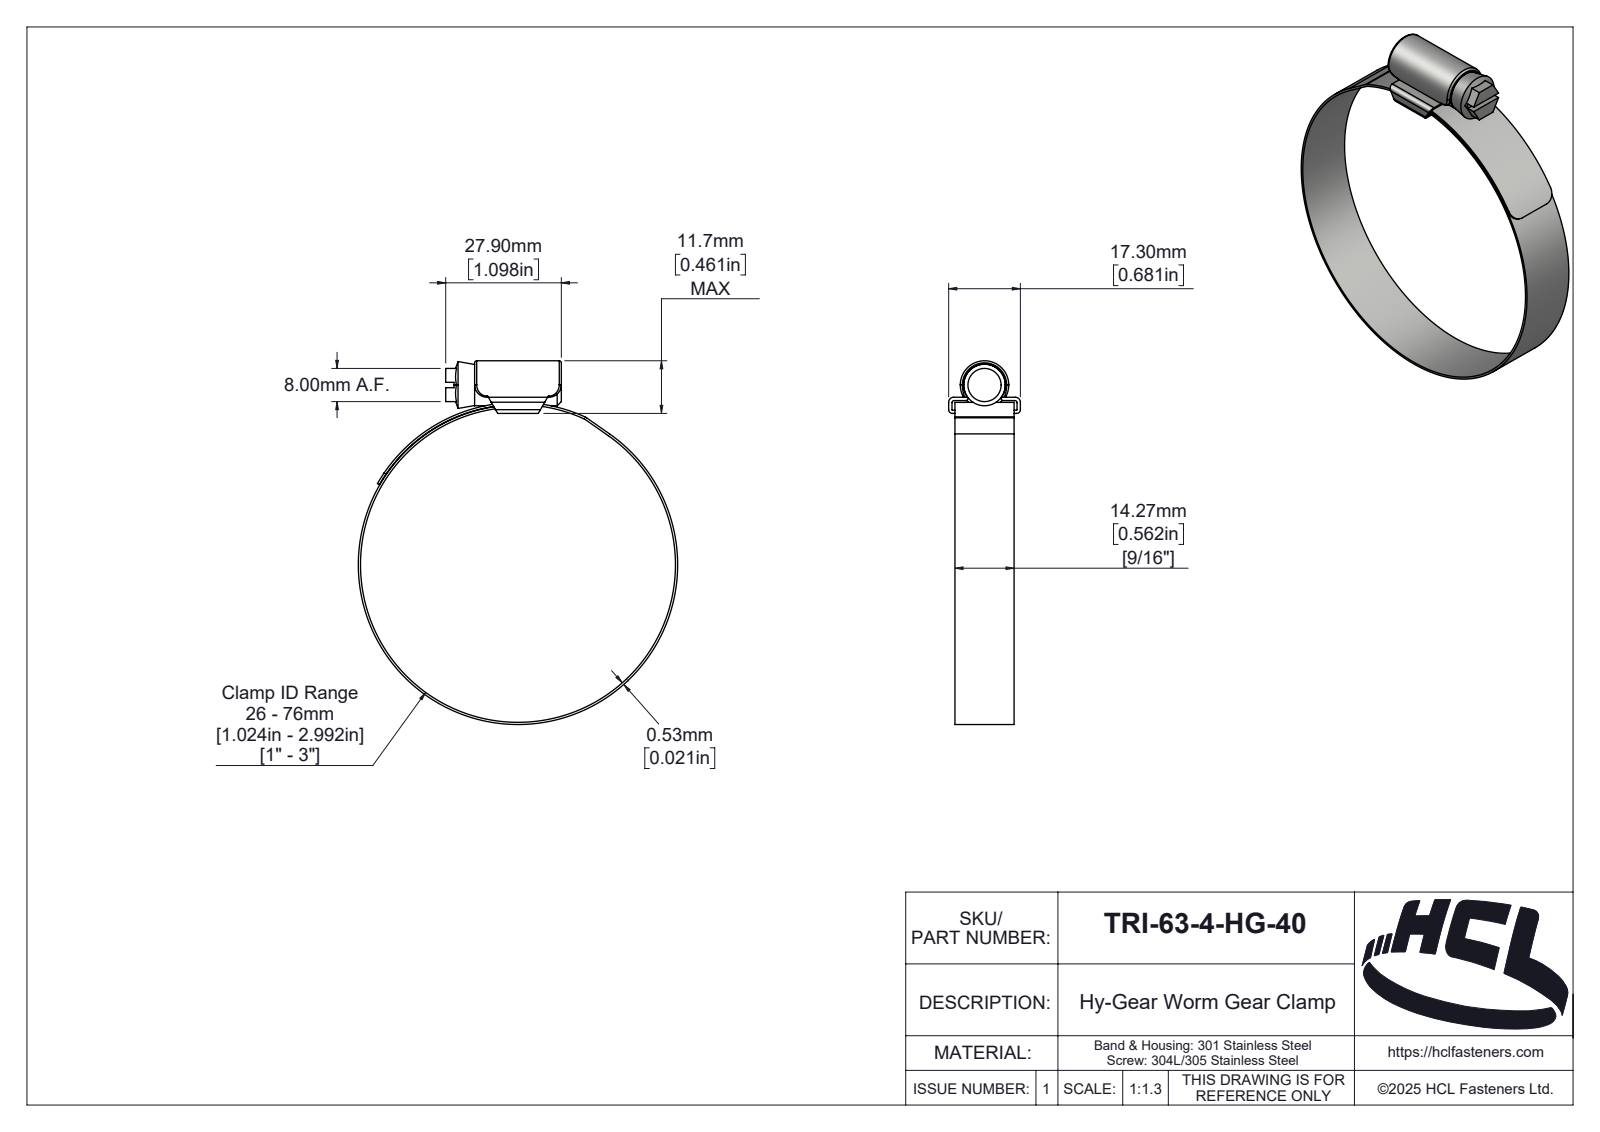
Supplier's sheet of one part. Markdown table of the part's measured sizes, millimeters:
| quantity | value |
| --- | --- |
| part name | TRI-50-0-HG-40 |
| STEP written by | SolidWorks 2025 (AUTOMOTIVE_DESIGN) |
| units | millimeters |
| bodies | 3 solids, 189 faces (39 planar, 89 cylindrical, 61 other) |
| overall size | 87.73 × 77.06 × 17.3 |
| volume | 4 919 mm³ |
| surface area | 11 131 mm² |
| round holes (diameter × count) | 76 × 1 |
| round bosses / shafts (diameter × count) | 77.06 × 1, 10 × 1 |
| partial cylindrical surfaces (radius × count) | 0.5 × 6, 3 × 4, 0.1 × 2, 0.9 × 2, 1.2 × 2, 0.46 × 1, 1.89 × 1, 2 × 1 |
| main face-to-face distances | 0.8, 3.1, 14.26, 0.53, 2.3, 3.9, 27.9, 1.52, 15.78, 16.5 |
